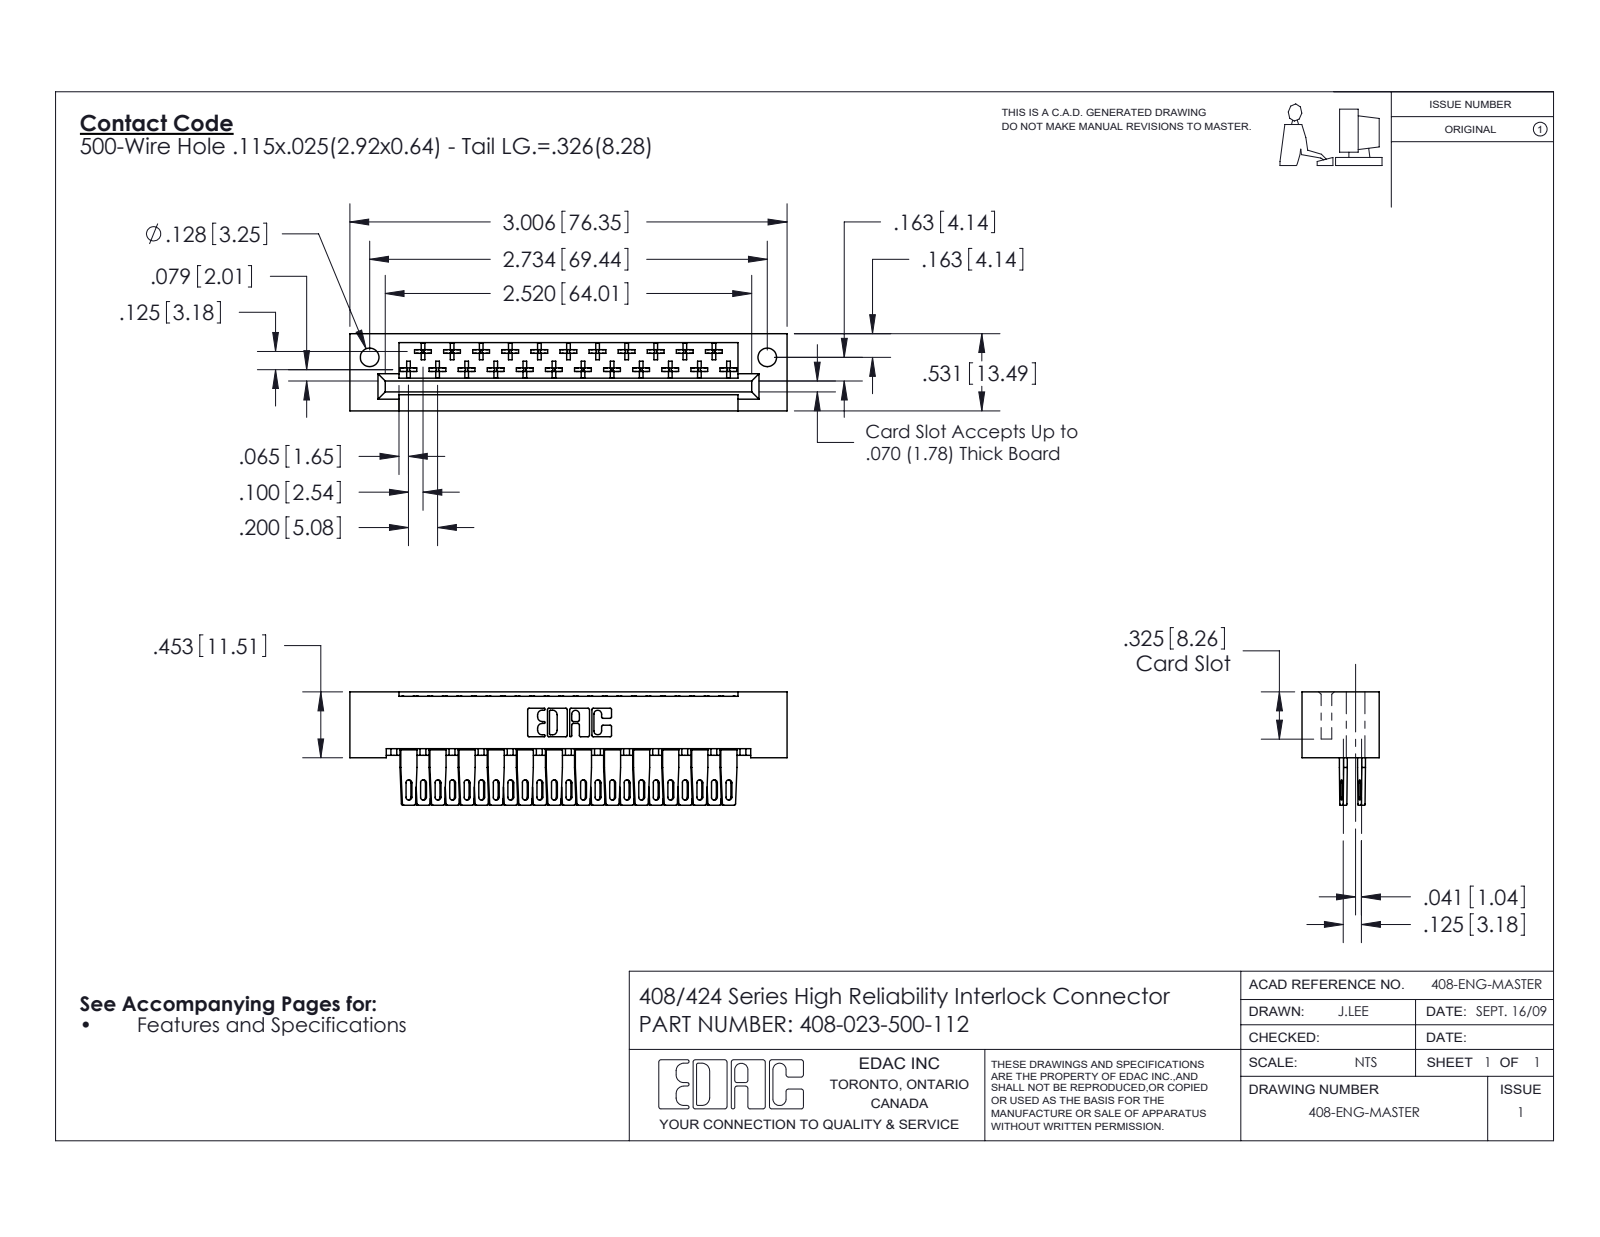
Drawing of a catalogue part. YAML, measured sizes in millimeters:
part_name: "408-290-001_408-290-100; 408-023-500-112; 408 Part_023 - 1"
step_written_by: "SolidWorks 2016 (CONFIG_CONTROL_DESIGN)"
units: millimeters
bodies: {solids: 24, faces: 1438, planar: 1022, cylindrical: 324, other: 92}
overall_size: [76.4, 19.8, 13.5]
volume: 9080
surface_area: 10970
round_holes:
  - {diameter: 3.3, count: 2}
partial_cylinders:
  - {radius: 0.3, count: 184}
  - {radius: 0.5, count: 46}
  - {radius: 0.5, count: 25}
  - {radius: 0.3, count: 22}
  - {radius: 0.2, count: 6}
  - {radius: 0.8, count: 6}
  - {radius: 0.7, count: 3}
face_to_face_distances: [13.5, 10.2, 0.6, 2.5, 3.2, 0.6, 6, 7.5, 6.6, 6.9]
hole_center_spacings: [69.4]
